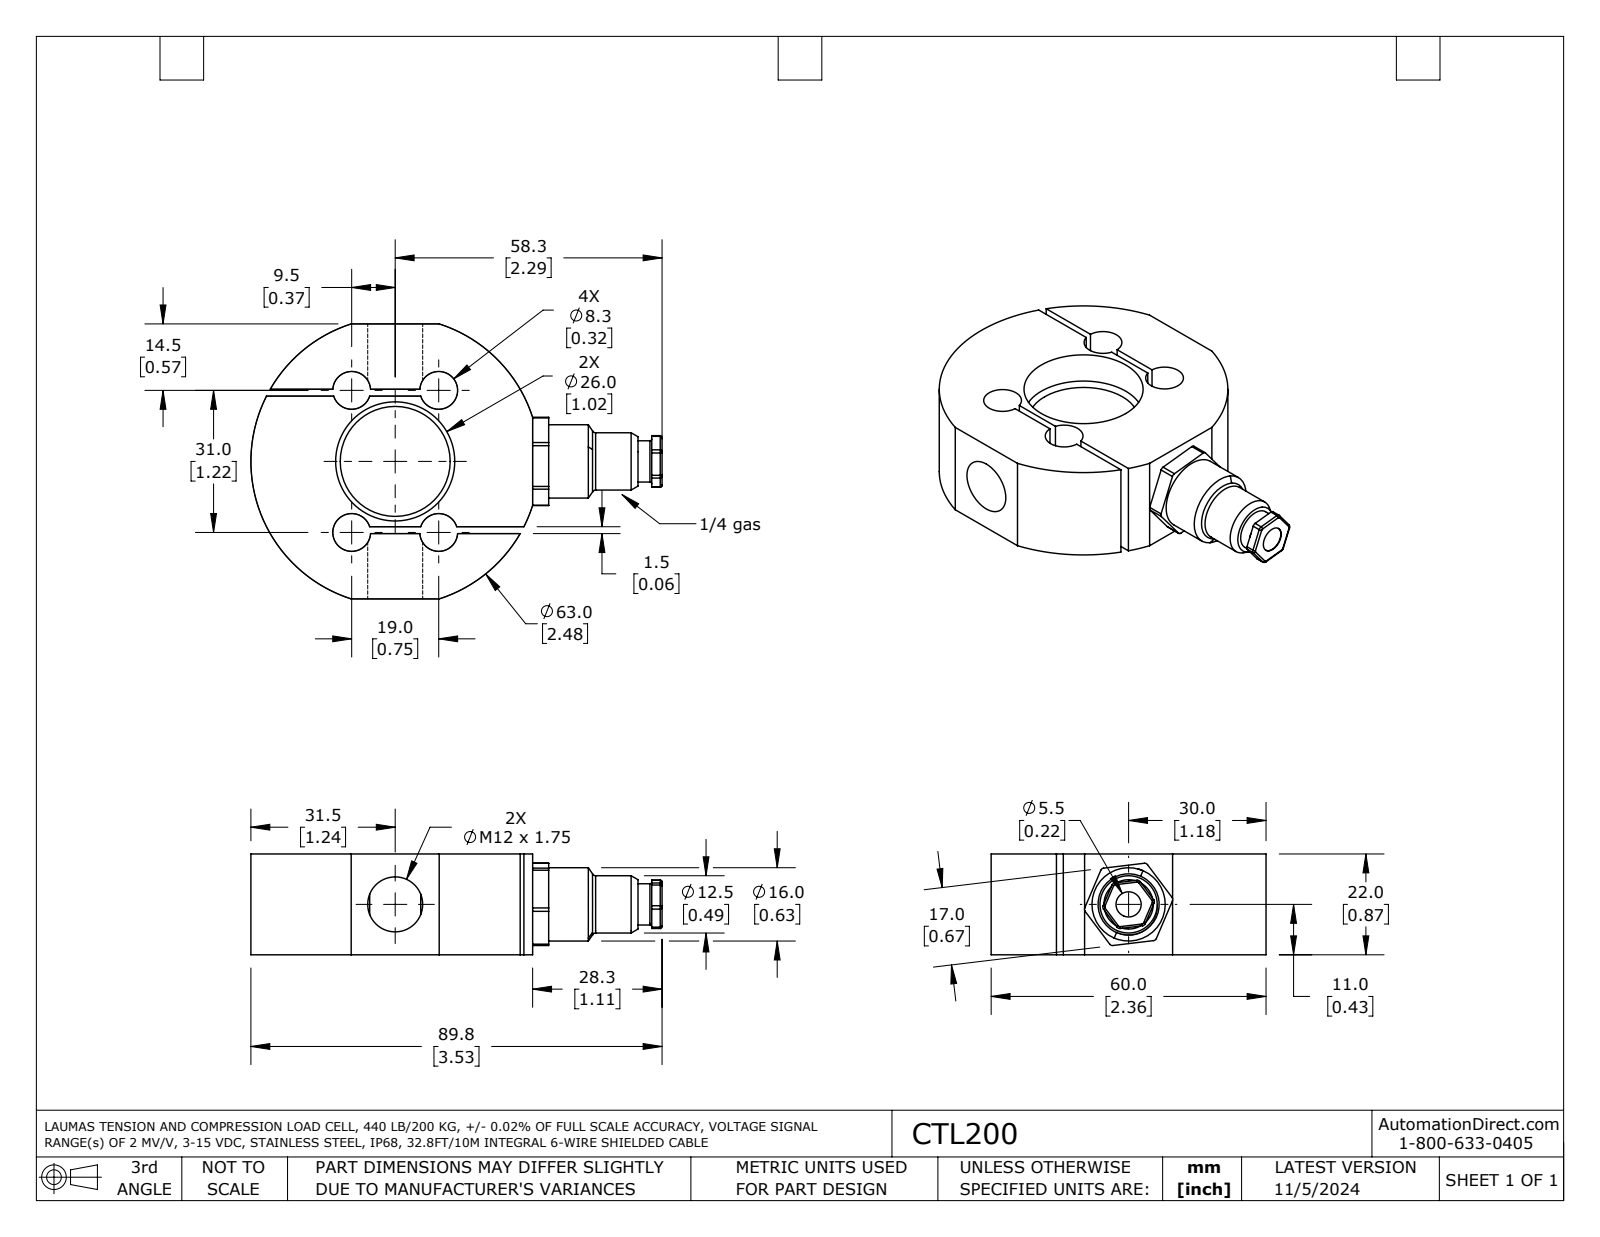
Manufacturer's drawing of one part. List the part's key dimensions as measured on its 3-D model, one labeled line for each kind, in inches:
Part name (STEP PRODUCT): CTL200
STEP written by: SolidWorks 2021 (AUTOMOTIVE_DESIGN)
Units: inches
Bodies: 2 solids, 114 faces (39 planar, 56 cylindrical, 19 other)
Overall size (bounding box): 3.533 × 2.362 × 0.866
Volume: 3.16 in³ · Surface area: 28.17 in²
Round holes (diameter × count): ⌀0.325 ×4, ⌀0.217 ×1, ⌀0.472 ×1, ⌀0.551 ×1, ⌀1.024 ×1
Round bosses / shafts (diameter × count): ⌀0.63 ×1, ⌀0.492 ×1, ⌀0.354 ×1
Partial cylindrical surfaces — rounded edges, fillets, slot ends (radius × count): R0.03 ×12, R0.016 ×6, R1.24 ×1
Main face-to-face distances: 0.866, 0.315, 0.551, 0.059, 1.181, 0.561, 0.62, 1.742, 1.801, 1.122
Hole centre spacings: 0.716, 0.748, 1.22, 1.431
